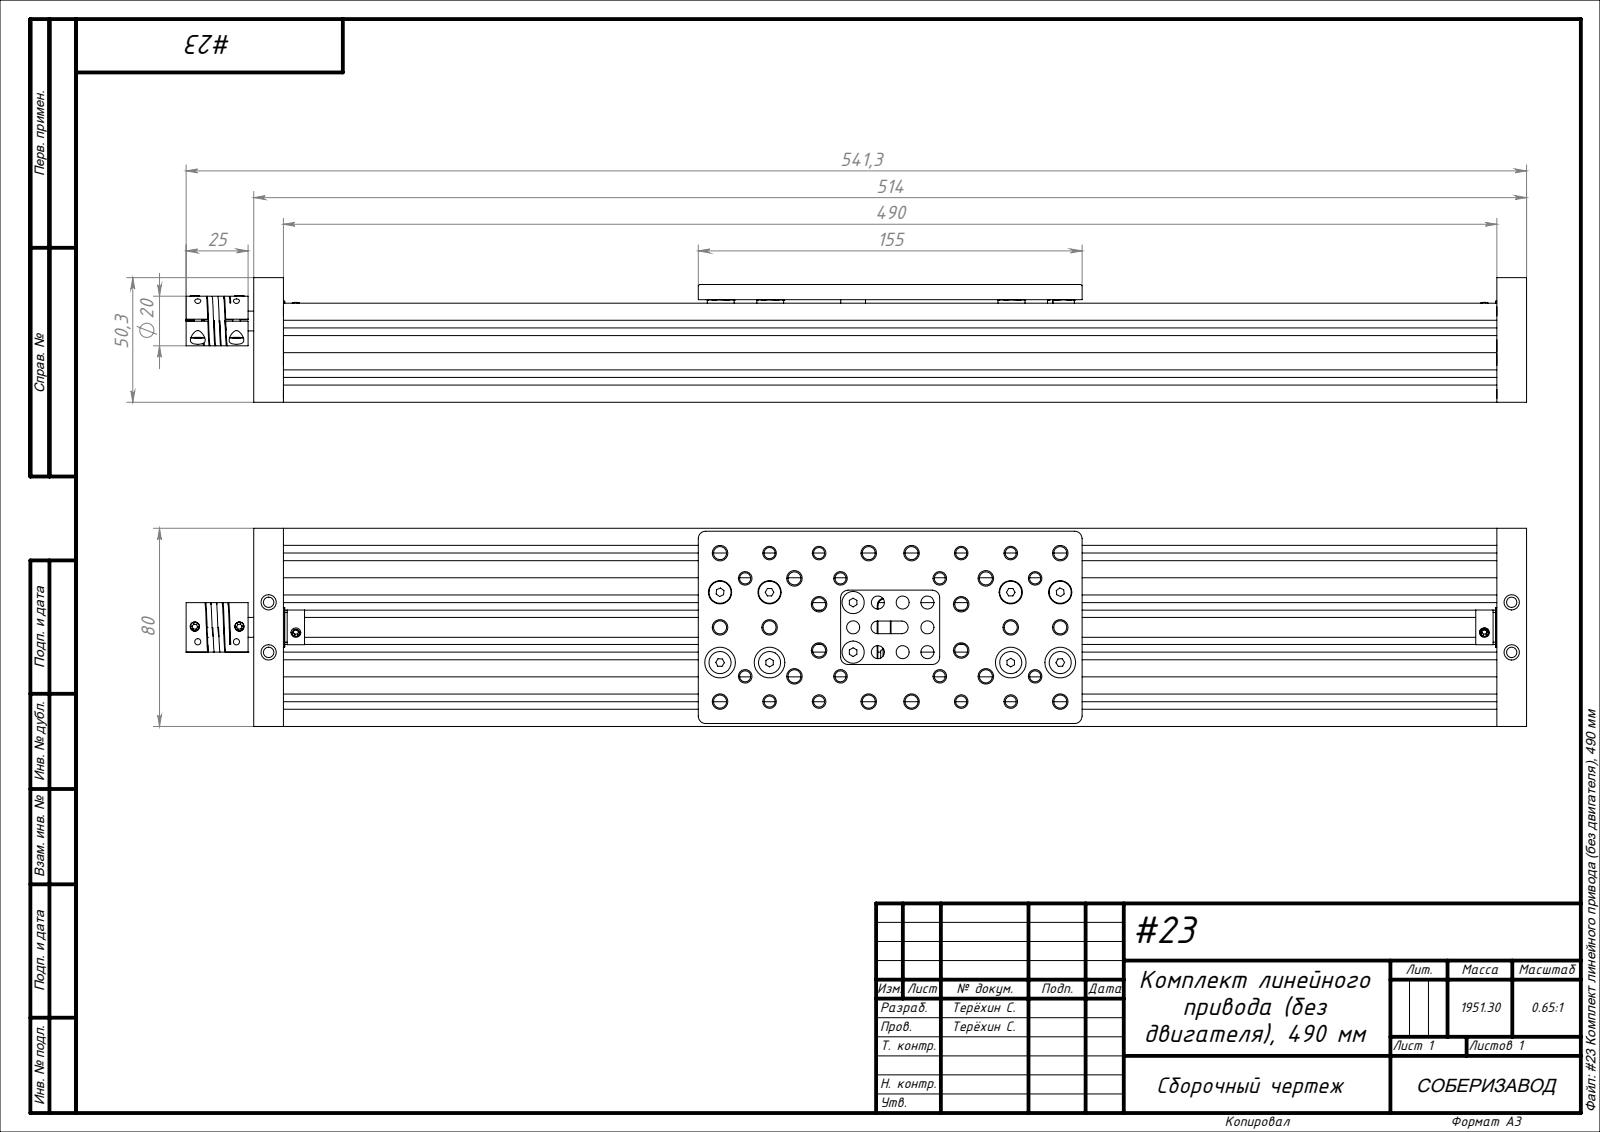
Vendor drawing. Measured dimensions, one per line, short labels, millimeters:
name: A246 Пластина портальная 77х155, удвоеная ширина (С-профиля)_00; A217 Трапецеидальный винт 8х531 мм, 4-х заходный, шаг 2 мм_00; A233 Ходовая гайка безлюфтовая 33x34_00; A199 Дистанционная втулка 5х3 мм (+8 more)
written by: SolidWorks 2021 (AUTOMOTIVE_DESIGN)
unit: mm
bodies: 171 solids, 4603 faces (1282 planar, 1432 cylindrical, 1889 other)
size: 541.3 × 80 × 50.3
volume: 660 938 mm³; area: 515 640 mm²
holes: 44× ⌀5.3, 16× ⌀4.5, 16× ⌀5, 11× ⌀4.2, 10× ⌀4.13, 10× ⌀5.15, 8× ⌀6.09, 8× ⌀7.8, 8× ⌀8.4, 8× ⌀8.65, 4× ⌀5.2, 4× ⌀7.2
bosses: 14× ⌀8, 10× ⌀7.83, 8× ⌀15.23, 8× ⌀8.95, 8× ⌀8.64, 8× ⌀7, 8× ⌀6.27, 8× ⌀6
rounds: 100× R0.25, 86× R0.2, 48× R2, 40× R1, 30× R0.3, 20× R1.4, 8× R3, 6× R1.5
face distances: 14.14, 28.28, 20, 12, 1.8, 12.34, 6, 14, 42.42, 2.83
hole spacings: 20, 15.6, 6.21, 10, 17.87, 22.39, 53.91, 20.03
